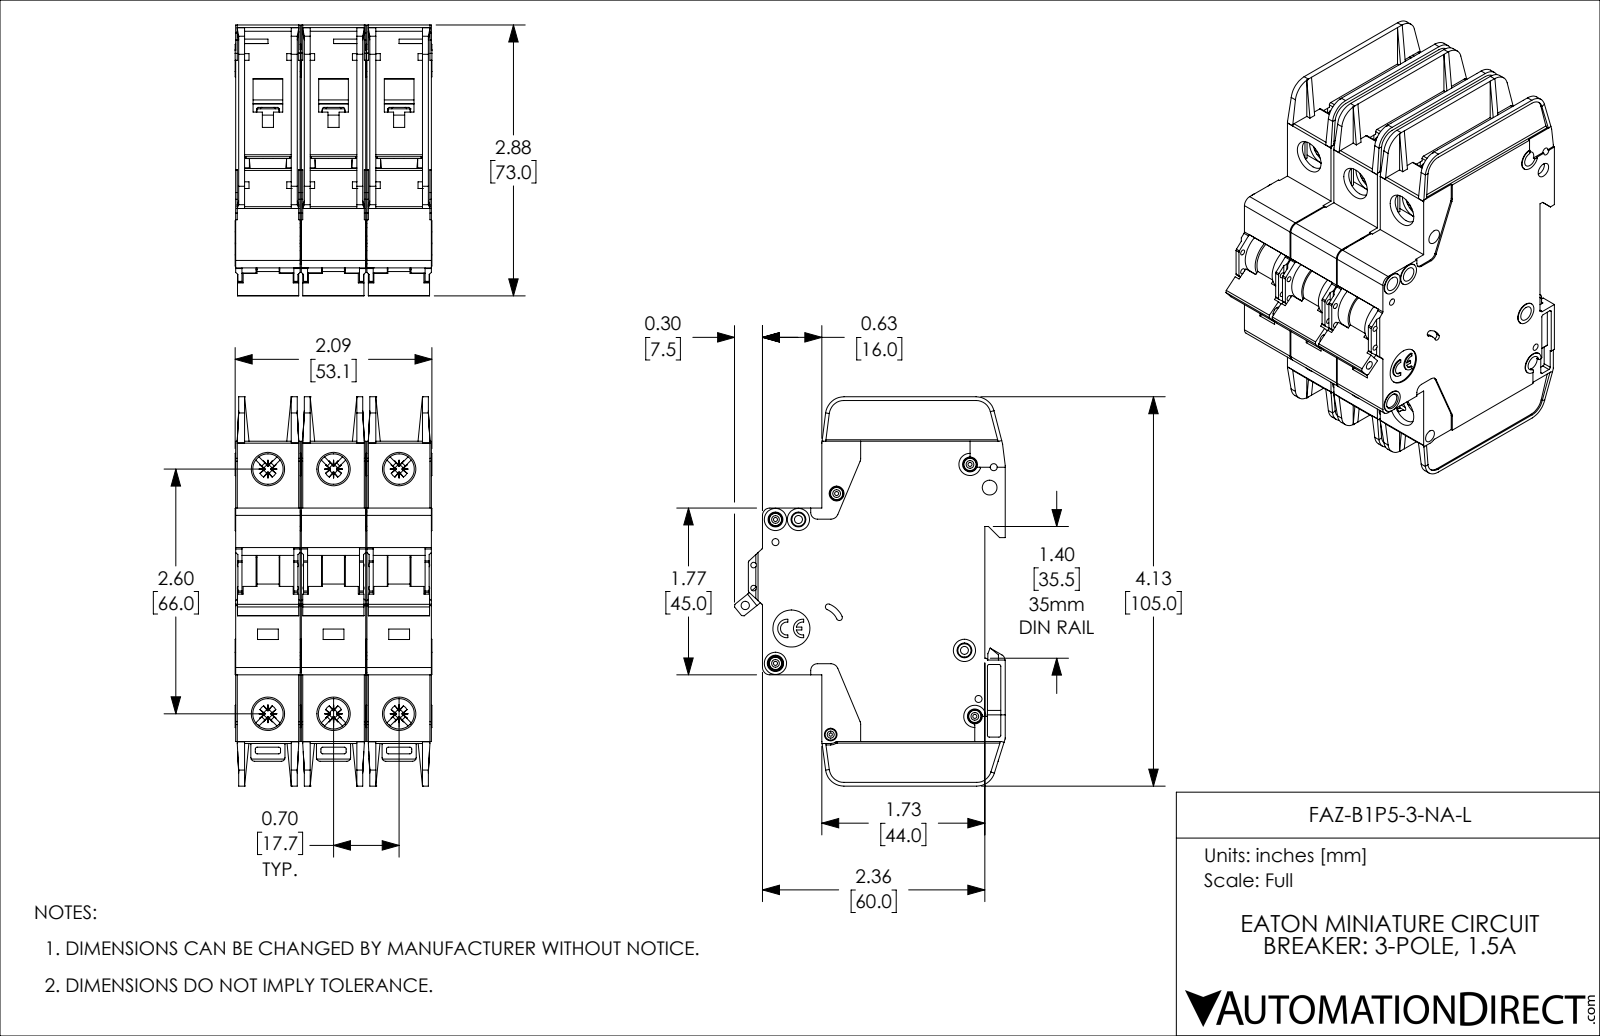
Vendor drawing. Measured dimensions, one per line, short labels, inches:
name: FAZ-B1P5-3-NA-L
written by: SolidWorks 2019 (AUTOMOTIVE_DESIGN)
unit: in
bodies: 3 solids, 3381 faces (2013 planar, 1071 cylindrical, 297 other)
size: 4.134 × 2.876 × 2.091
volume: 14.05 in³; area: 123 in²
holes: 8× ⌀0.157, 6× ⌀0.323, 5× ⌀0.043, 4× ⌀0.075, 2× ⌀0.059, 2× ⌀0.085, 1× ⌀0.035, 1× ⌀0.089, 1× ⌀0.098, 1× ⌀0.134, 1× ⌀0.394
bosses: 5× ⌀0.13, 4× ⌀0.236, 4× ⌀0.118, 3× ⌀0.098
rounds: 72× R0.02, 30× R0.016, 18× R0.039, 12× R0.043, 12× R0.079, 6× R0.008, 6× R0.01, 6× R0.028
face distances: 0.697, 0.047, 1.394, 0.685, 0.591, 1.382, 0.744, 0.65, 0.106, 0.094
hole spacings: 0.697, 2.69, 2.598, 0.244, 0.537, 0.87, 1.394, 2.948
